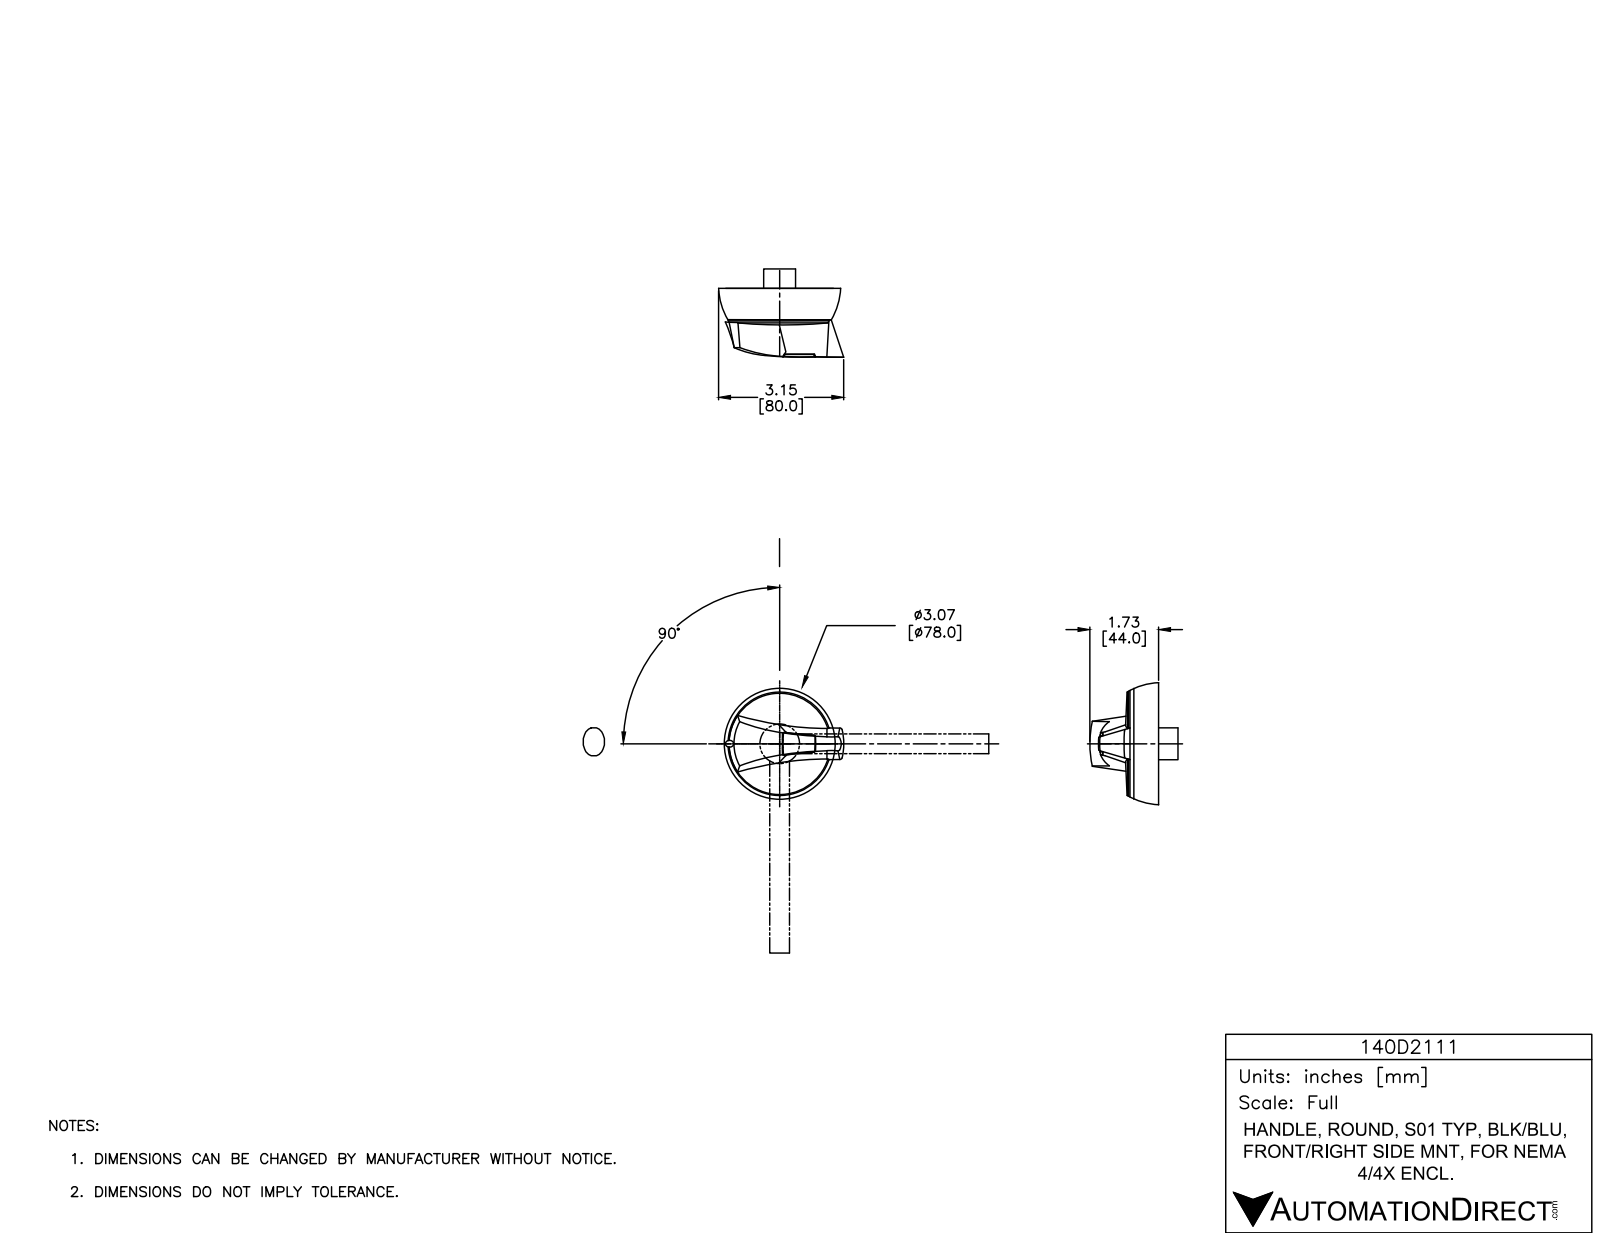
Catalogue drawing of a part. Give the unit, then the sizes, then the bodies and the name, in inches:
Units: inches
Overall size (bounding box): 3.144 × 3.07 × 2.028
Round holes (diameter × count): ⌀0.157 ×6, ⌀0.425 ×4, ⌀0.03 ×3, ⌀0.169 ×2, ⌀0.339 ×2, ⌀0.362 ×2, ⌀0.189 ×1, ⌀2.992 ×1
Round bosses / shafts (diameter × count): ⌀0.02 ×11, ⌀0.315 ×4, ⌀0.089 ×3, ⌀0.069 ×3, ⌀0.228 ×2, ⌀2.819 ×1, ⌀2.701 ×1, ⌀2.63 ×1
Partial cylindrical surfaces — rounded edges, fillets, slot ends (radius × count): R0.01 ×221, R0.015 ×20, R0.034 ×20, R0.03 ×15, R0.025 ×3, R7.874 ×2, R0.01 ×1, R0.079 ×1
Main face-to-face distances: 0.024, 0.622, 1.539, 0.917, 0.035, 0.61, 1.528, 0.598, 1.516, 0.244
Hole centre spacings: 0.961, 0.309, 1.098, 1.102, 1.203, 1.575, 1.881, 1.922
Volume: 8.078 in³ · Surface area: 57.01 in²
Bodies: 9 solids, 1345 faces (711 planar, 526 cylindrical, 108 other)
Part name (STEP PRODUCT): 140D2111
STEP written by: SolidWorks 2015 (AUTOMOTIVE_DESIGN)
